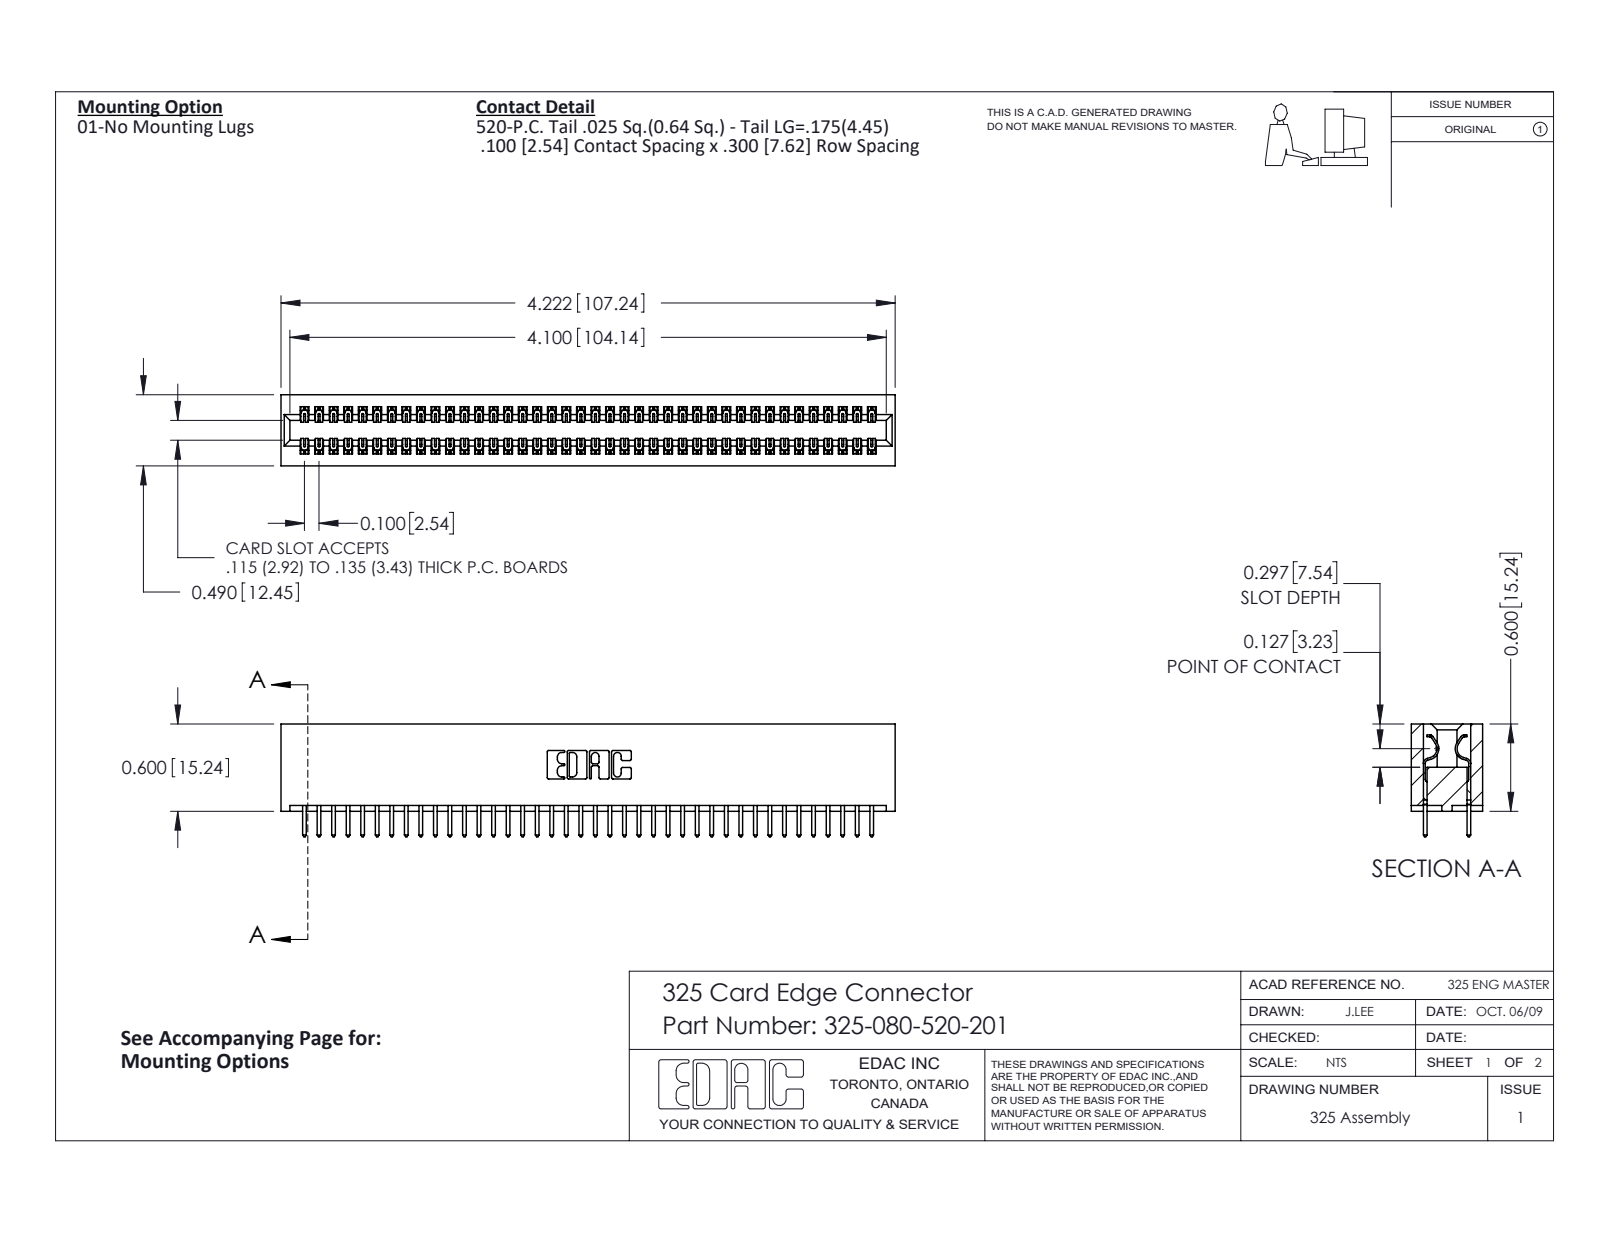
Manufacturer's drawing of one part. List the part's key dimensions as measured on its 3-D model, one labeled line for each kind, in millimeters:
Part name (STEP PRODUCT): 325 Part_Lugless; 325-292-001_325-293-120; 325-080-520-201
STEP written by: SolidWorks 2016 (CONFIG_CONTROL_DESIGN)
Units: millimetres
Bodies: 81 solids, 4266 faces (2946 planar, 1320 cylindrical, 0 other)
Overall size (bounding box): 107.2 × 19.7 × 12.4
Volume: 14 400 mm³ · Surface area: 17 900 mm²
Partial cylindrical surfaces — rounded edges, fillets, slot ends (radius × count): R0.2 ×120, R0.3 ×80, R0.3 ×22, R0.2 ×6, R0.8 ×6, R0.7 ×3, R0.4 ×2, R0.6 ×2
Main face-to-face distances: 2.1, 10.3, 7.6, 12.4, 2.7, 9.7, 0.6, 8.3, 7, 14.2
